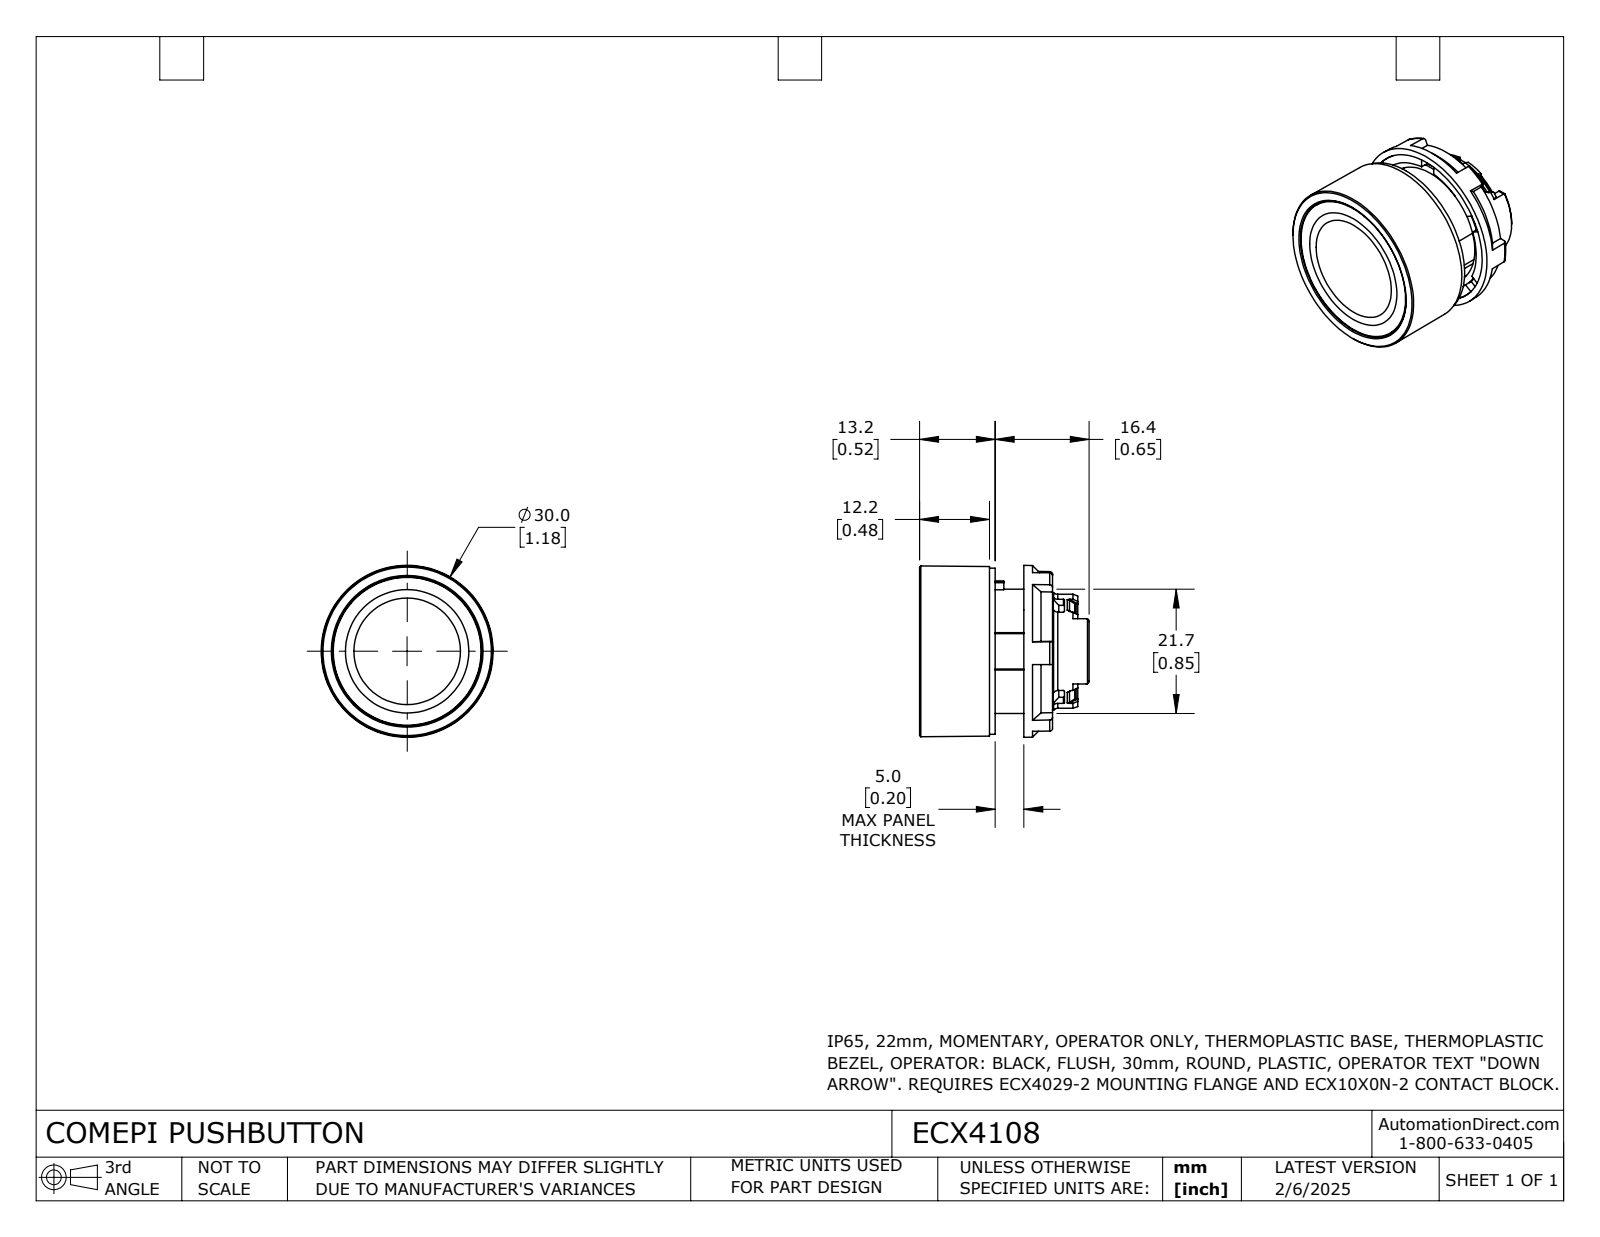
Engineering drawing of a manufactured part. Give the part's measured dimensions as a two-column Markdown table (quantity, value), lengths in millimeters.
| quantity | value |
| --- | --- |
| part name | ECX4108 |
| STEP written by | SolidWorks 2024 (CONFIG_CONTROL_DESIGN) |
| units | millimeters |
| bodies | 3 solids, 398 faces (134 planar, 111 cylindrical, 153 other) |
| overall size | 30 × 30 × 29.6 |
| volume | 7 730 mm³ |
| surface area | 10 680 mm² |
| round holes (diameter × count) | 13.5 × 1, 18.1 × 1, 22 × 1 |
| round bosses / shafts (diameter × count) | 29 × 1, 25.8 × 1, 24.5 × 1, 21.7 × 1, 20.5 × 1, 20 × 1, 19 × 1, 18.5 × 1 |
| partial cylindrical surfaces (radius × count) | 0.2 × 24, 0.5 × 8, 0.3 × 2, 7.4 × 1, 8.7 × 1, 8.8 × 1, 9.3 × 1 |
| main face-to-face distances | 10.4, 1, 11, 12, 6, 10, 5, 11.4, 13, 5.5 |
